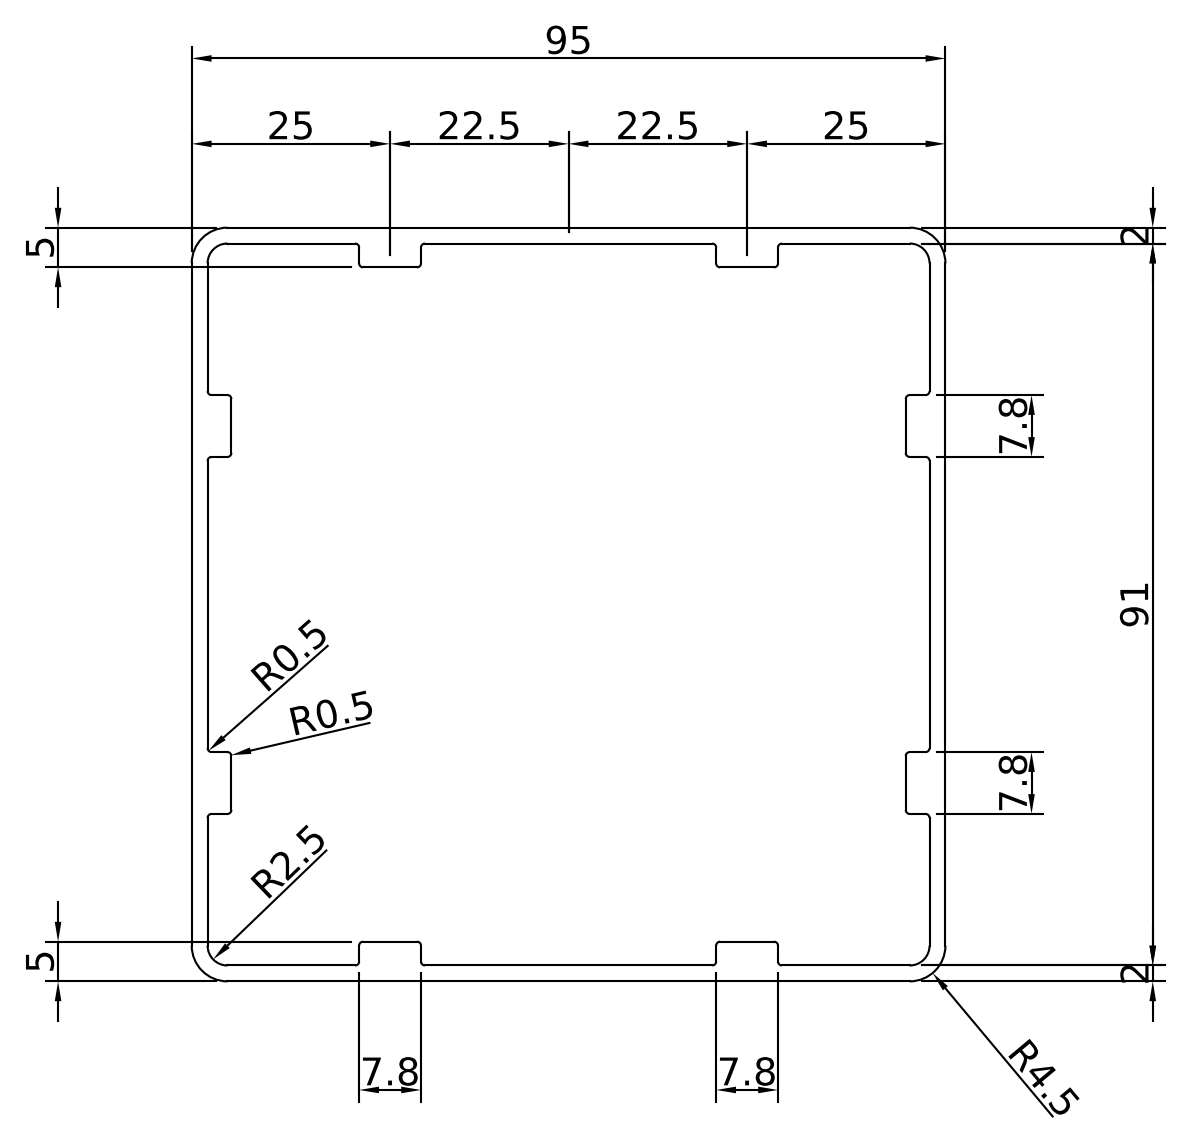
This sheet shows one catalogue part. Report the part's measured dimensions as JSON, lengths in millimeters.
{"part_name": "BPRQQ0000025", "step_written_by": "Autodesk Inventor 2019 (AUTOMOTIVE_DESIGN)", "units": "millimeters", "bodies": {"solids": 1, "faces": 82, "planar": 42, "cylindrical": 40, "other": 0}, "overall_size": [100, 95, 95], "volume_mm3": 91918, "surface_area_mm2": 79150, "partial_cylinders_radius": [[0.5, 32], [2.5, 4], [4.5, 4]], "face_to_face_distances": [2, 93, 95, 91, 5, 90, 3, 88, 85, 21.1]}
